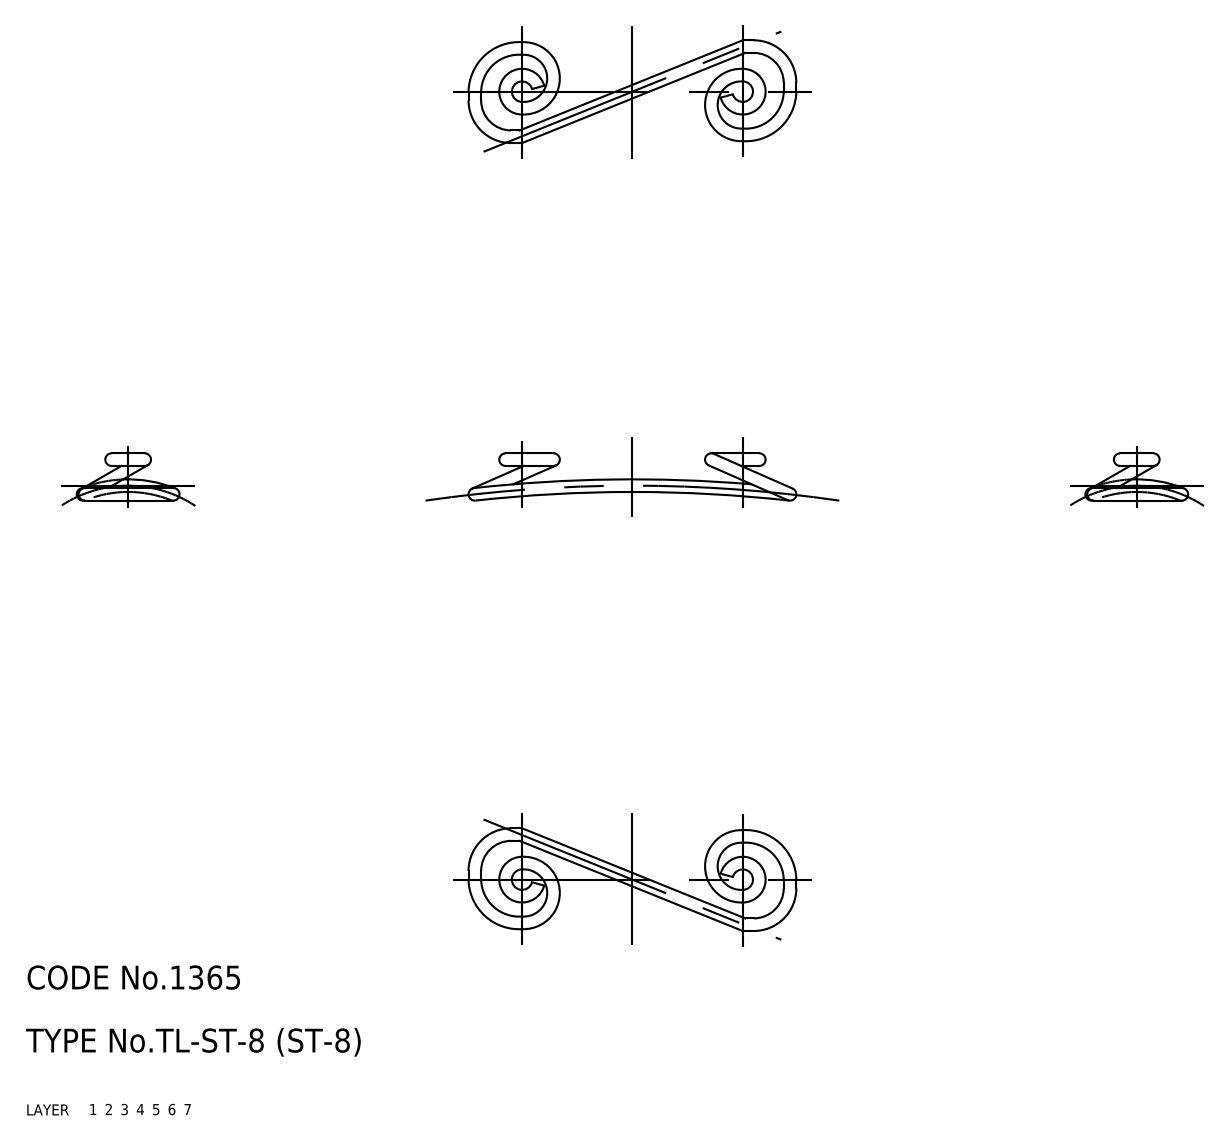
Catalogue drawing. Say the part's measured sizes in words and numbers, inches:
The part is named "spring". Its 3-D file was written by "CADfix (AUTOMOTIVE_DESIGN)". It is 1 solid with 24 faces: 0 planar, 0 cylindrical and 24 other. Overall it measures 1.638 by 0.498 by 0.237 inches. Its volume is 0.014 cubic inches and its surface area 0.876 square inches.
